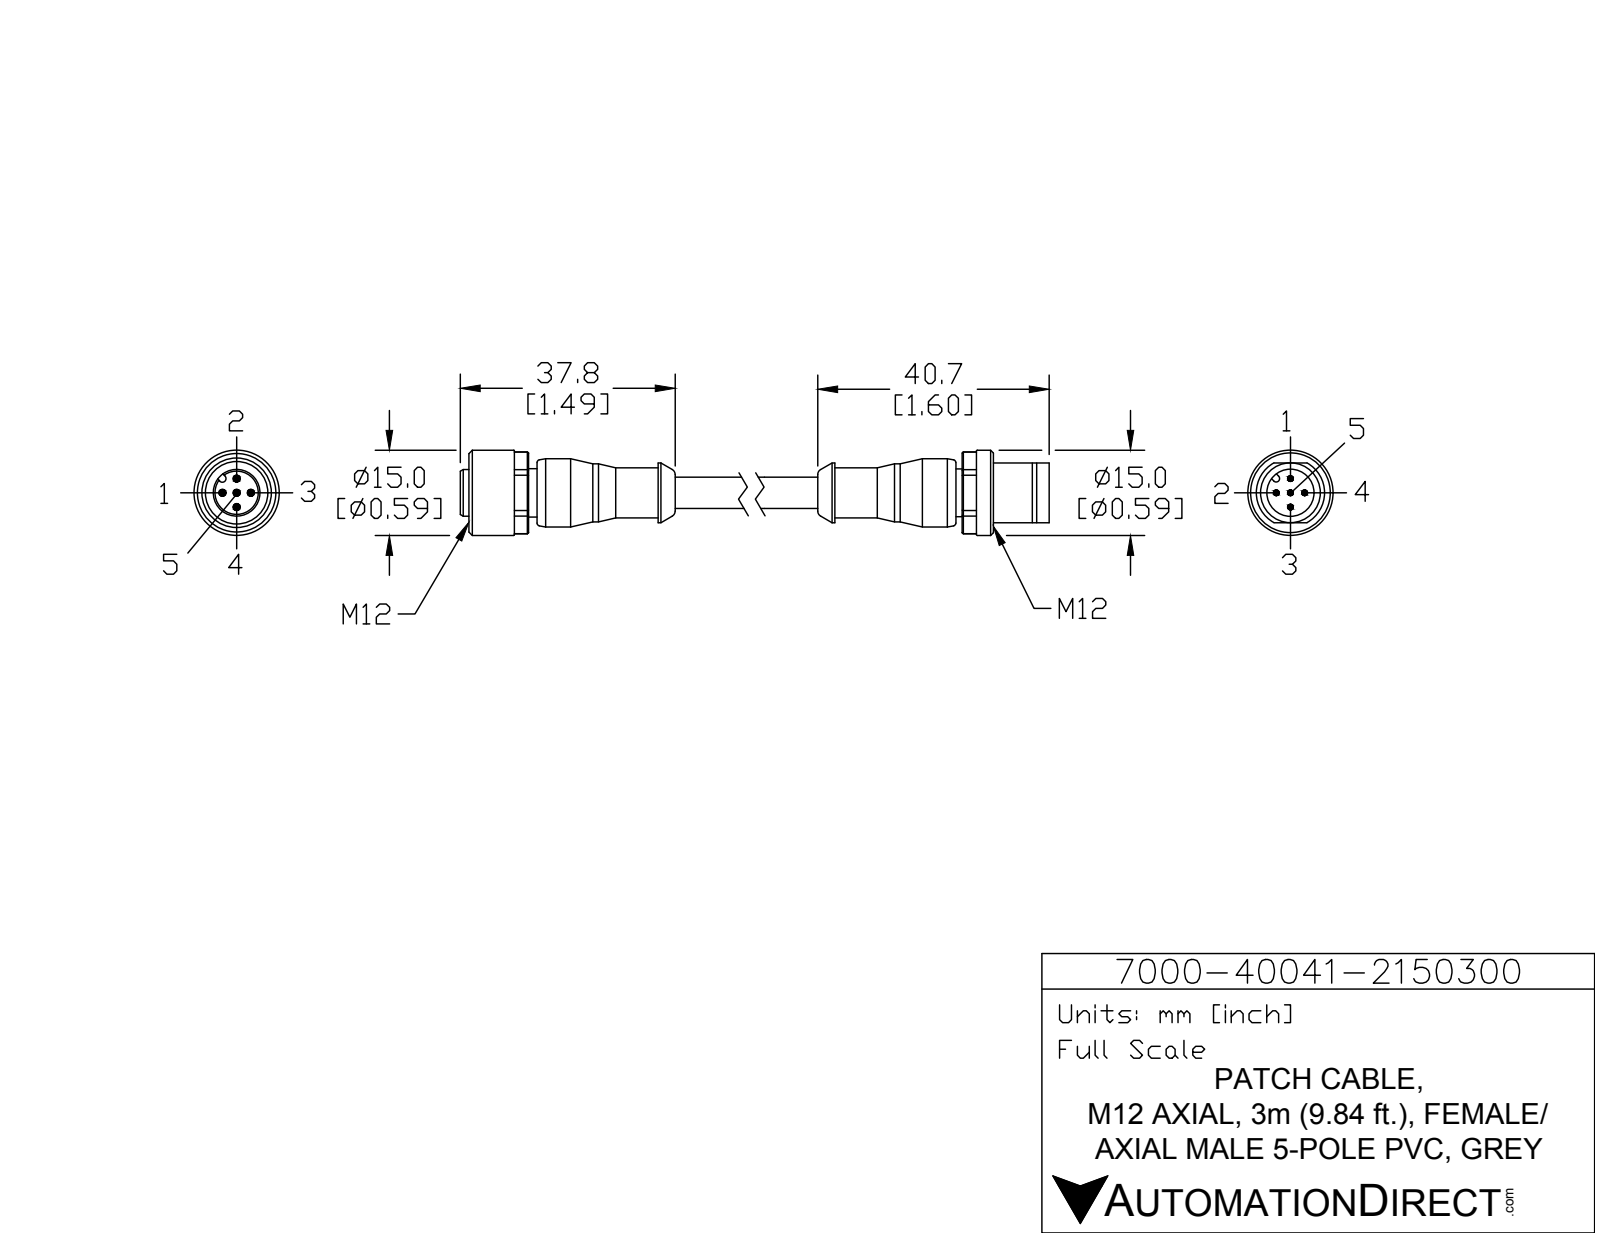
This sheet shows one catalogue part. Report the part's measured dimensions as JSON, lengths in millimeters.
{"part_name": "7000-40041-2150300_F; 7000-40041-2150300; 7000-40041-2150300_M", "step_written_by": "SolidWorks 2018 (AUTOMOTIVE_DESIGN)", "units": "millimeters", "bodies": {"solids": 2, "faces": 196, "planar": 60, "cylindrical": 73, "other": 63}, "overall_size": [124.2, 15, 15], "volume_mm3": 8000, "surface_area_mm2": 5164, "round_holes": [[1.2, 5], [8.3, 1], [11, 1]], "round_bosses_or_shafts": [[1, 5], [15, 1], [12, 1], [10.5, 1], [10.2, 1], [8.8, 1], [8.5, 1], [8.4, 1]], "partial_cylinders_radius": [[0.6, 1], [0.7, 1], [7.2, 1]], "face_to_face_distances": [13, 3, 96.9, 10.5, 106.3, 12, 102.4, 7.5, 1.5, 2.5], "hole_center_spacings": [2.5, 3.5, 5]}
